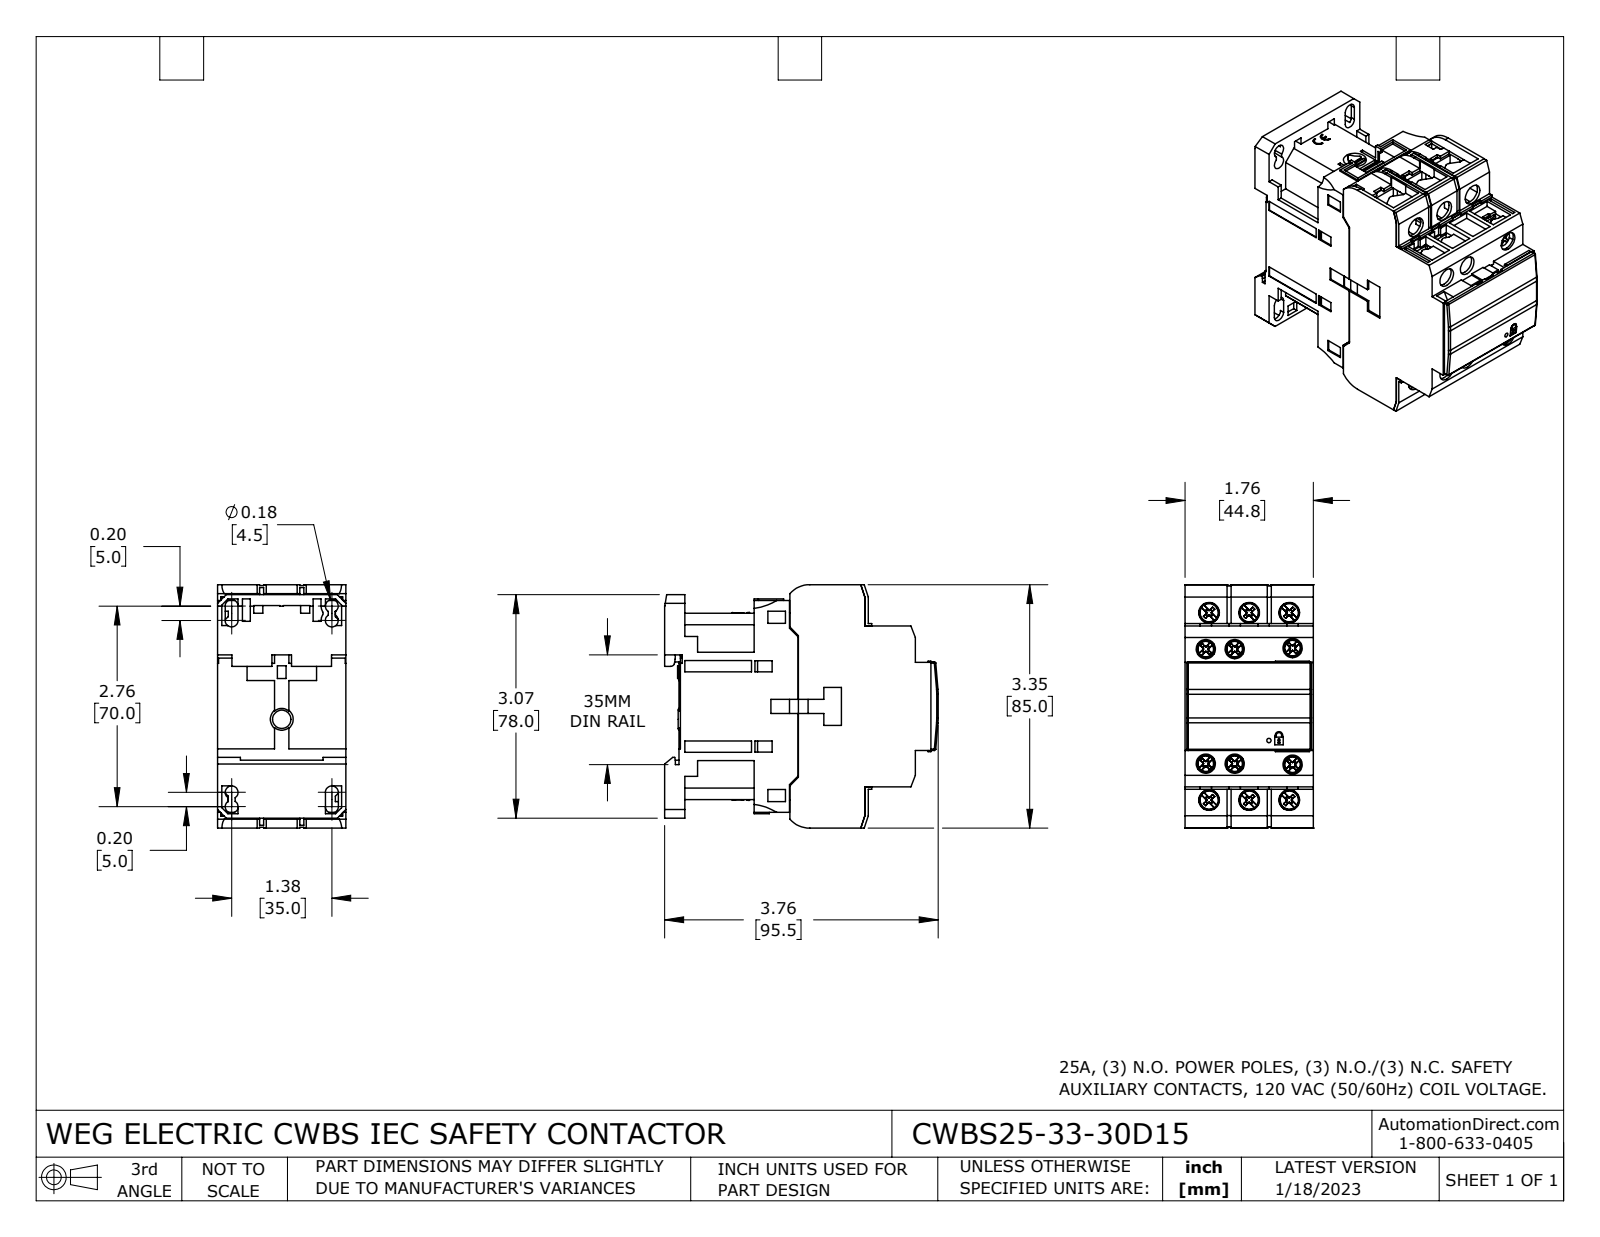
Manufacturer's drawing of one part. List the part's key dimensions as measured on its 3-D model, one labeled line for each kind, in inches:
Part name (STEP PRODUCT): CWBS25-33-30D15
STEP written by: SolidWorks 2021 (CONFIG_CONTROL_DESIGN)
Units: inches
Bodies: 42 solids, 2461 faces (1808 planar, 446 cylindrical, 207 other)
Overall size (bounding box): 3.76 × 3.346 × 1.764
Volume: 14.49 in³ · Surface area: 108.8 in²
Round holes (diameter × count): ⌀0.124 ×6, ⌀0.142 ×6, ⌀0.264 ×6, ⌀0.283 ×6, ⌀0.177 ×4, ⌀0.059 ×1
Round bosses / shafts (diameter × count): ⌀0.201 ×6, ⌀0.169 ×6, ⌀0.157 ×6, ⌀0.138 ×6, ⌀0.107 ×4, ⌀0.107 ×2
Partial cylindrical surfaces — rounded edges, fillets, slot ends (radius × count): R0.02 ×42, R0.028 ×24, R0.071 ×12, R0.081 ×12, R0.964 ×12, R1.079 ×12, R2.128 ×12, R3.127 ×12
Main face-to-face distances: 1.764, 0.047, 1.691, 0.132, 1.823, 0.024, 0.217, 3.445, 0.276, 1.717
Hole centre spacings: 0.551, 2.633, 2.575, 0.165, 0.174, 0.197, 0.398, 0.488
